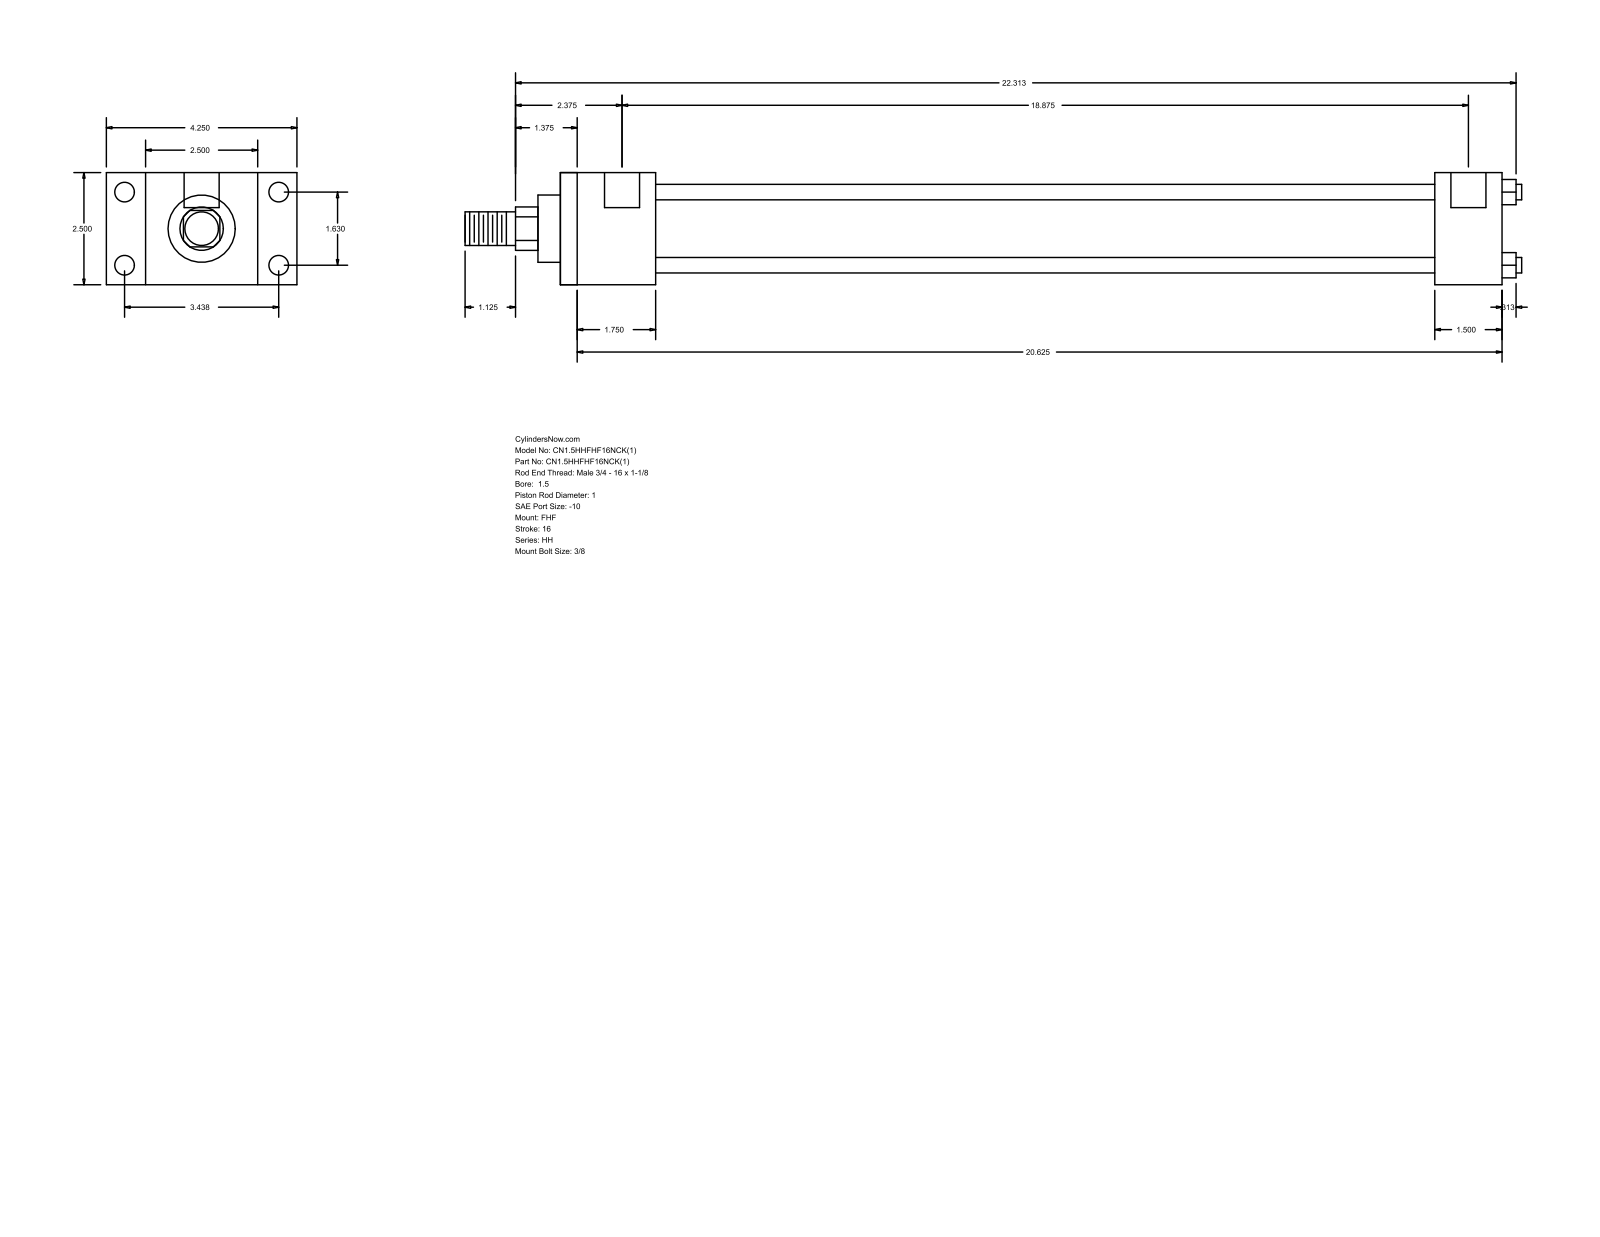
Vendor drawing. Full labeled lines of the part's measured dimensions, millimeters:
Part name (STEP PRODUCT): HH_FHF__0150_1
STEP written by: GSSL Pune (CONFIG_CONTROL_DESIGN)
Units: millimetres
Bodies: 0 solids, 88 faces (60 planar, 28 cylindrical, 0 other)
Overall size (bounding box): 598.49 × 107.95 × 63.5
Round holes (diameter × count): ⌀5.56 ×4, ⌀11.13 ×4, ⌀19.84 ×2
Round bosses / shafts (diameter × count): ⌀8.76 ×4, ⌀44.45 ×1, ⌀38.1 ×1, ⌀25.4 ×1, ⌀19.05 ×1
Partial cylindrical surfaces — rounded edges, fillets, slot ends (radius × count): R12.29 ×1
Main face-to-face distances: 63.5, 22.23, 85.73, 53.98, 107.96, 533.4, 479.42, 38.1, 495.3, 441.32
Hole centre spacings: 1.59, 41.4, 87.32, 96.64, 481.01, 482.6, 479.42
